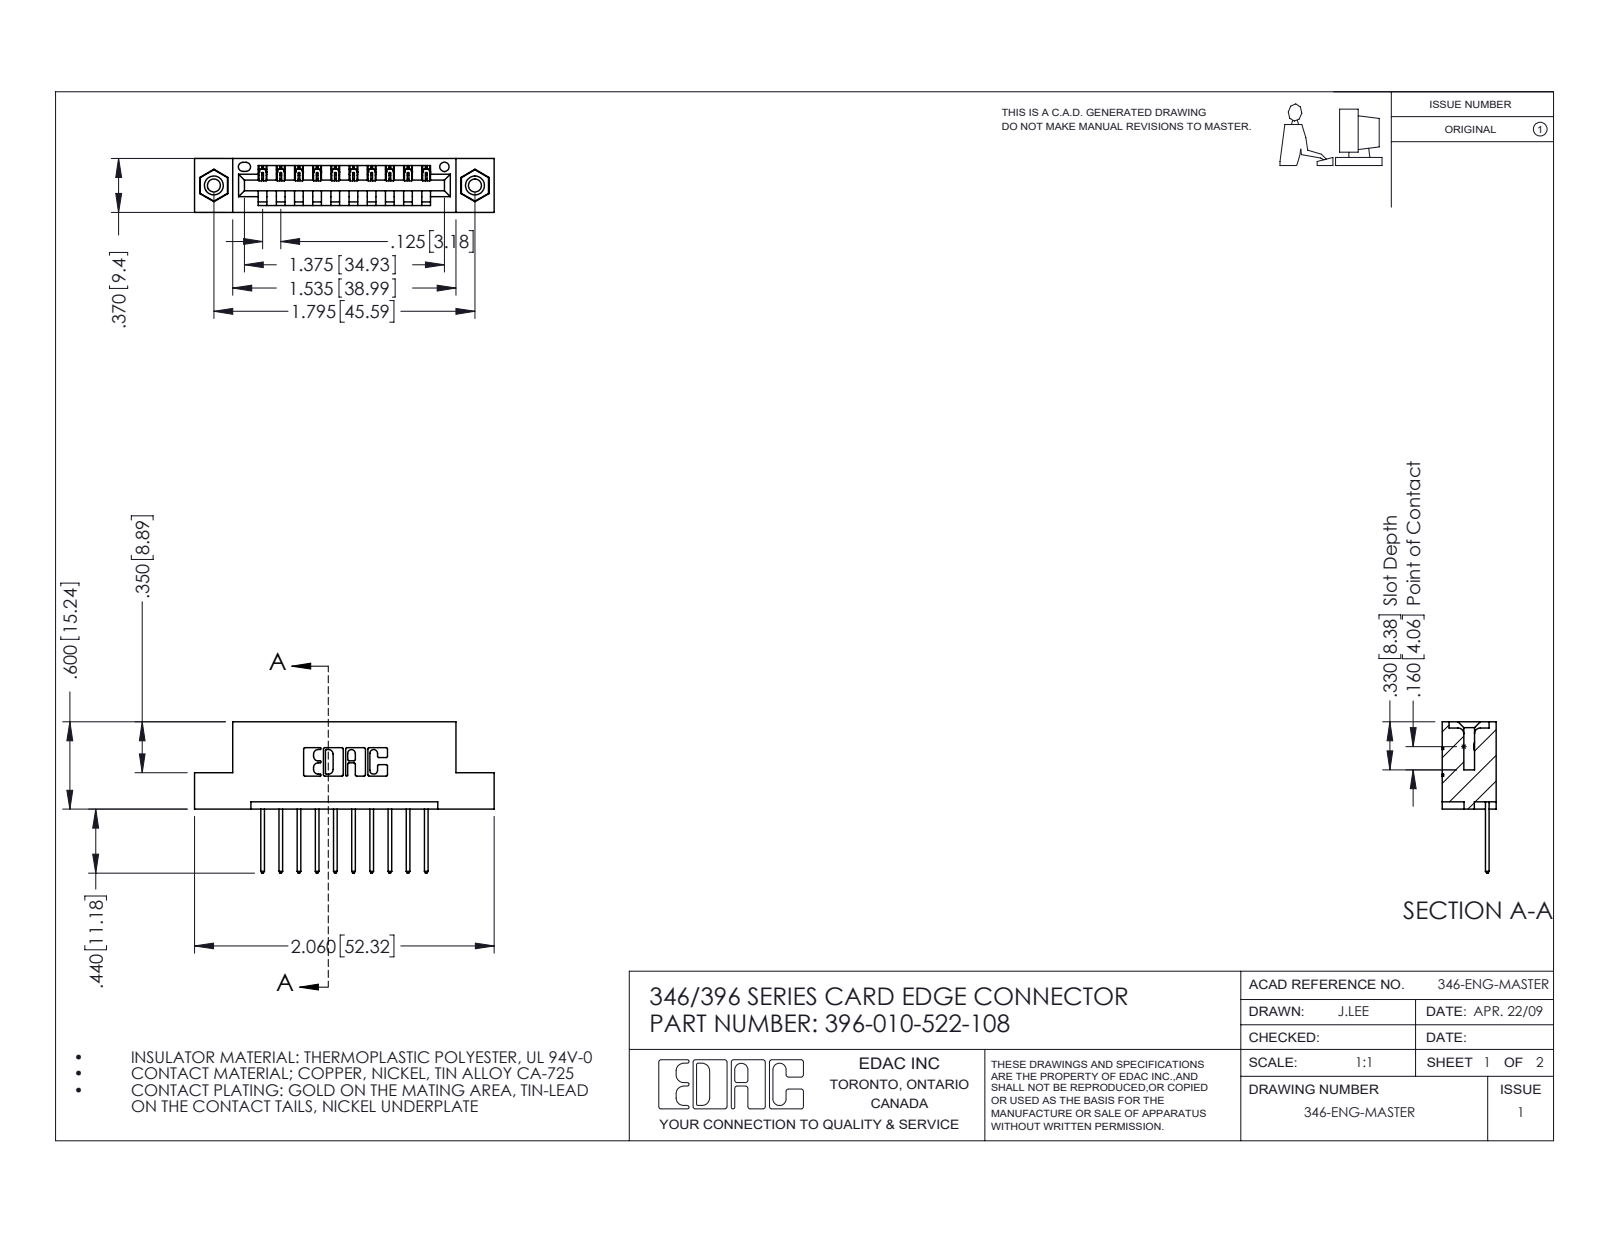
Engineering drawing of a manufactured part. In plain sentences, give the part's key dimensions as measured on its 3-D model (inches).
The part is named "396-010-522-108; 346 Part_Flush Mounting Lugs - 0.156 Dia-TI; 345-292-001_345-293-122; 345-250-001_345-250-003-102". Its 3-D file was written by "SolidWorks 2016 (CONFIG_CONTROL_DESIGN)". It is 13 solids with 762 faces: 508 planar, 238 cylindrical and 16 other. Overall it measures 2.06 by 1.04 by 0.37 inches. Its volume is 0.292 cubic inches and its surface area 8.821 square inches. Round holes: 2 of diameter 0.089, 2 of diameter 0.125, 2 of diameter 0.156, 1 of diameter 0.064. Round bosses or shafts: 2 of diameter 0.155. Partial cylindrical surfaces (rounded edges, fillets, slot ends): 22 of radius 0.01, 20 of radius 0.006, 20 of radius 0.01, 6 of radius 0.007, 6 of radius 0.031, 3 of radius 0.026, 2 of radius 0.031, 2 of radius 0.04. The main face-to-face distances are 0.25, 0.048, 0.322, 0.37, 0.072, 0.298, 0.025, 0.148, 0.222, 0.1. The hole center spacings are 0.246, 1.59, 1.795.
